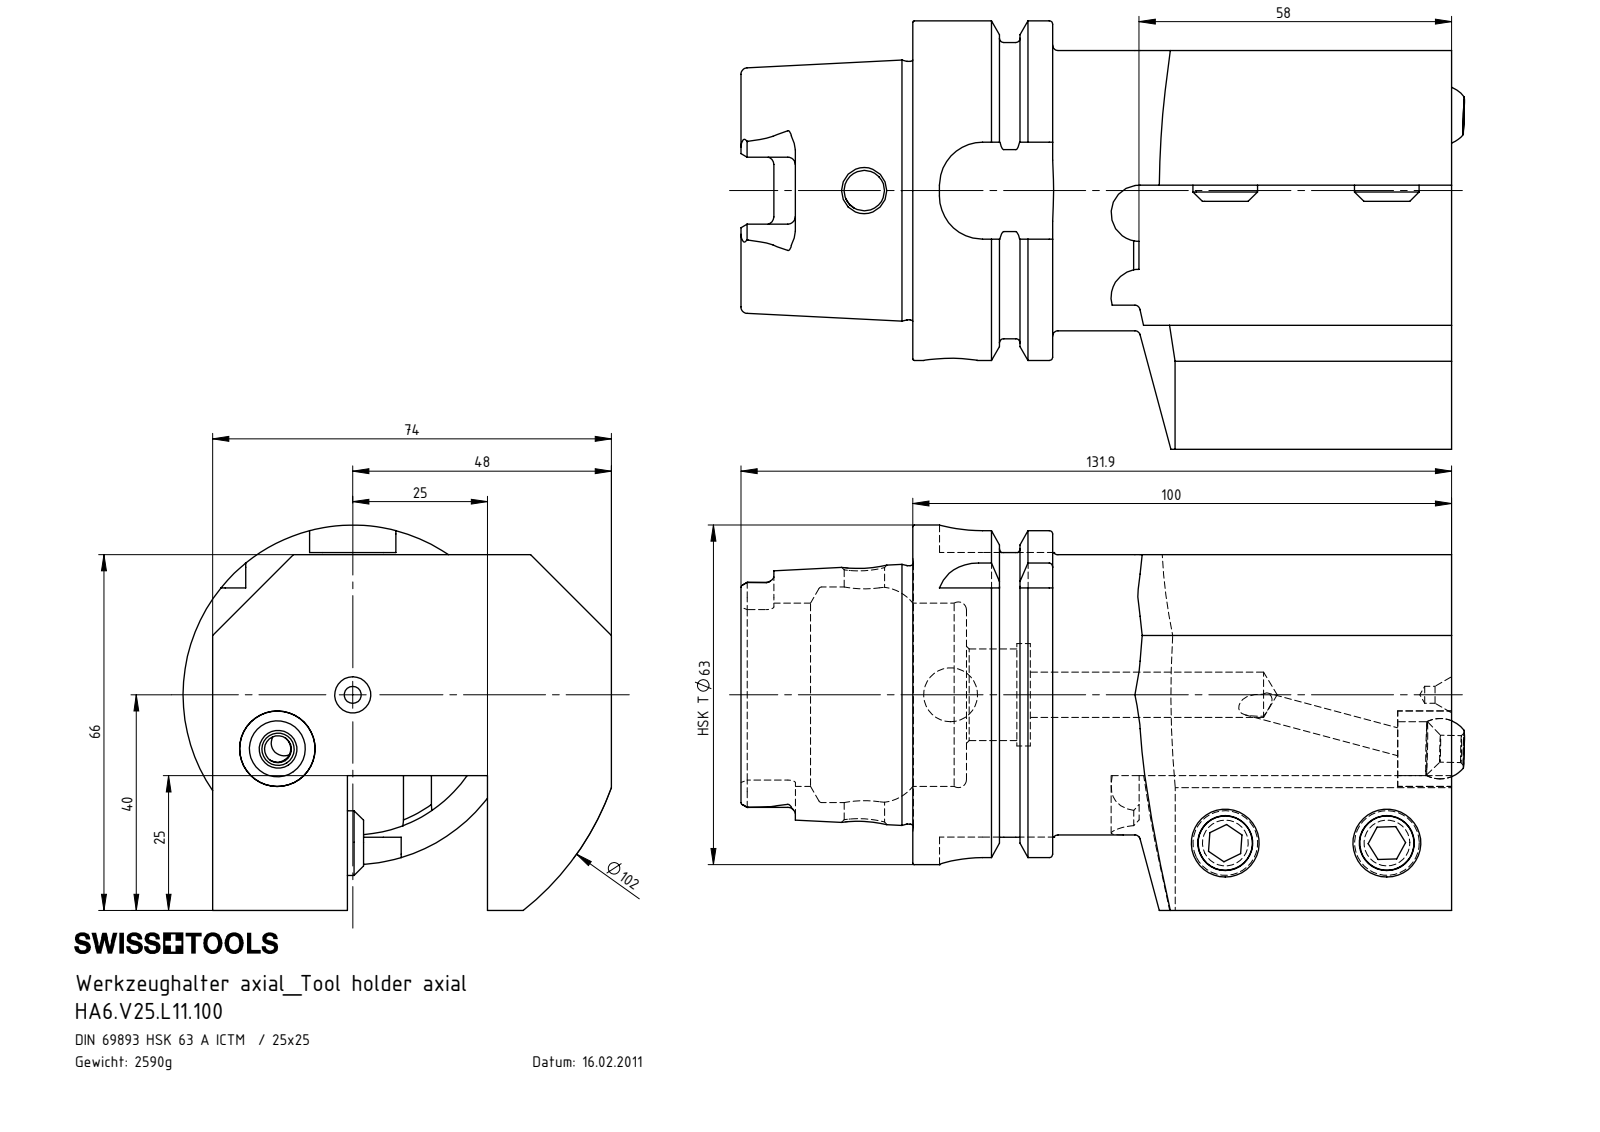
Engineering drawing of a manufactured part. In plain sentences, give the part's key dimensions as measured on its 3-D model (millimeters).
The part is named "HA6.V25.L11.100; KU1-U14.001.012_1; HA6-V25.L11.100_B; ISO 4026 - M12 x 25 (+2 more)". Its 3-D file was written by "SolidWorks 2017 (AUTOMOTIVE_DESIGN)". It is 5 solids with 241 faces: 76 planar, 68 cylindrical and 97 other. Overall it measures 134.71 by 79.5 by 71.5 millimeters. Its volume is 330 516 cubic millimeters and its surface area 52 432 square millimeters. Round holes: 2 of diameter 5, 2 of diameter 10, 2 of diameter 10.2, 1 of diameter 3.15, 1 of diameter 7.5, 1 of diameter 8.4, 1 of diameter 14, 1 of diameter 17, 1 of diameter 19, 1 of diameter 34, 1 of diameter 40. Round bosses or shafts: 2 of diameter 12, 1 of diameter 63, 1 of diameter 54.95, 1 of diameter 52, 1 of diameter 47.94. Partial cylindrical surfaces (rounded edges, fillets, slot ends): 6 of radius 1.4, 4 of radius 2.88, 4 of radius 8, 2 of radius 5.2, 1 of radius 51. The main face-to-face distances are 25, 66, 41, 23, 74, 51, 49, 26, 100, 16. The hole center spacings are 17.2, 30, 57.94, 85.54.
